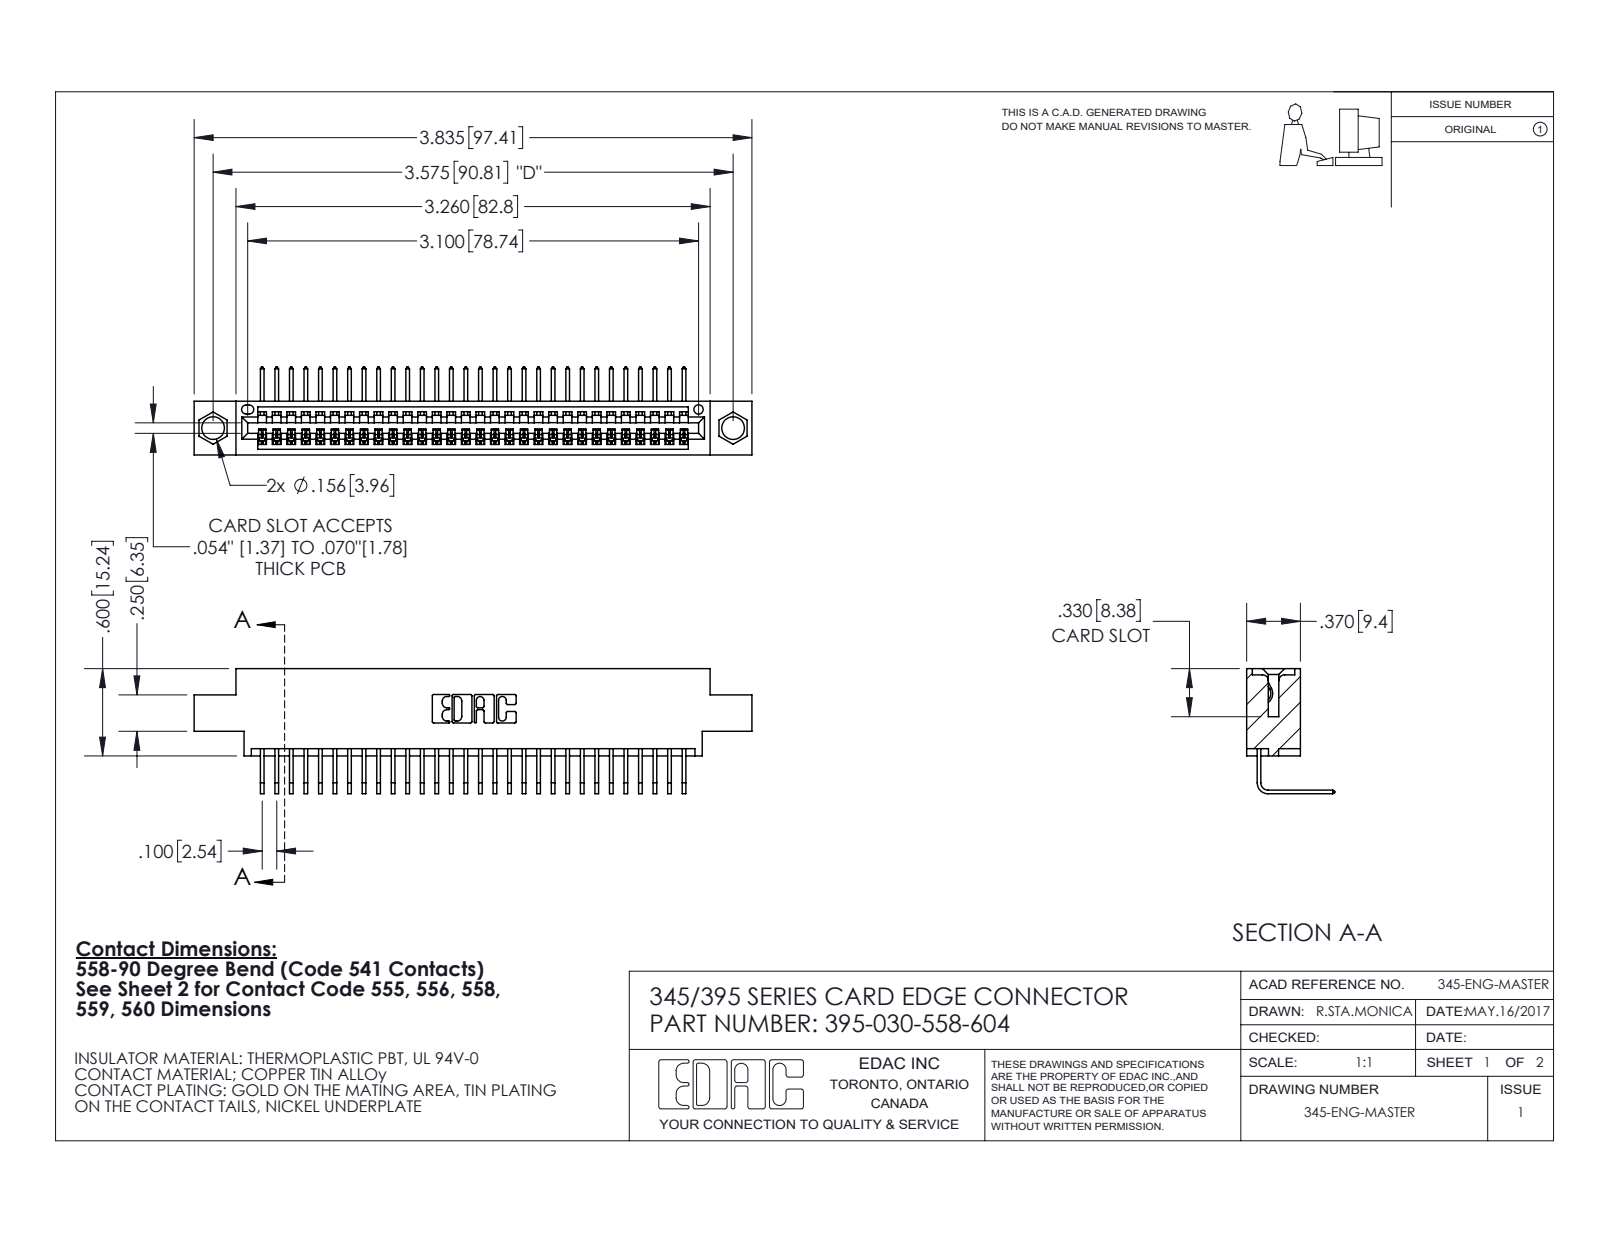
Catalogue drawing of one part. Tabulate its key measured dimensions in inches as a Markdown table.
| quantity | value |
| --- | --- |
| part name | 395-030-558-604; 345-292-001_558 Tail - 2; 345 Part_0.170 Offset - 0.156 Dia-TI |
| STEP written by | SolidWorks 2020 (CONFIG_CONTROL_DESIGN) |
| units | inches |
| bodies | 31 solids, 1944 faces (1358 planar, 586 cylindrical, 0 other) |
| overall size | 3.835 × 0.859 × 0.605 |
| volume | 0.551 in³ |
| surface area | 19.22 in² |
| round holes (diameter × count) | 0.156 × 2, 0.064 × 1 |
| partial cylindrical surfaces (radius × count) | 0.006 × 60, 0.01 × 22, 0.007 × 6, 0.031 × 6, 0.026 × 3, 0.031 × 2, 0.04 × 2, 0.014 × 1 |
| main face-to-face distances | 0.072, 0.298, 0.37, 0.2, 0.098, 0.272, 0.025, 0.225, 0.175, 0.149 |
| hole center spacings | 0.27, 3.34, 3.575 |
